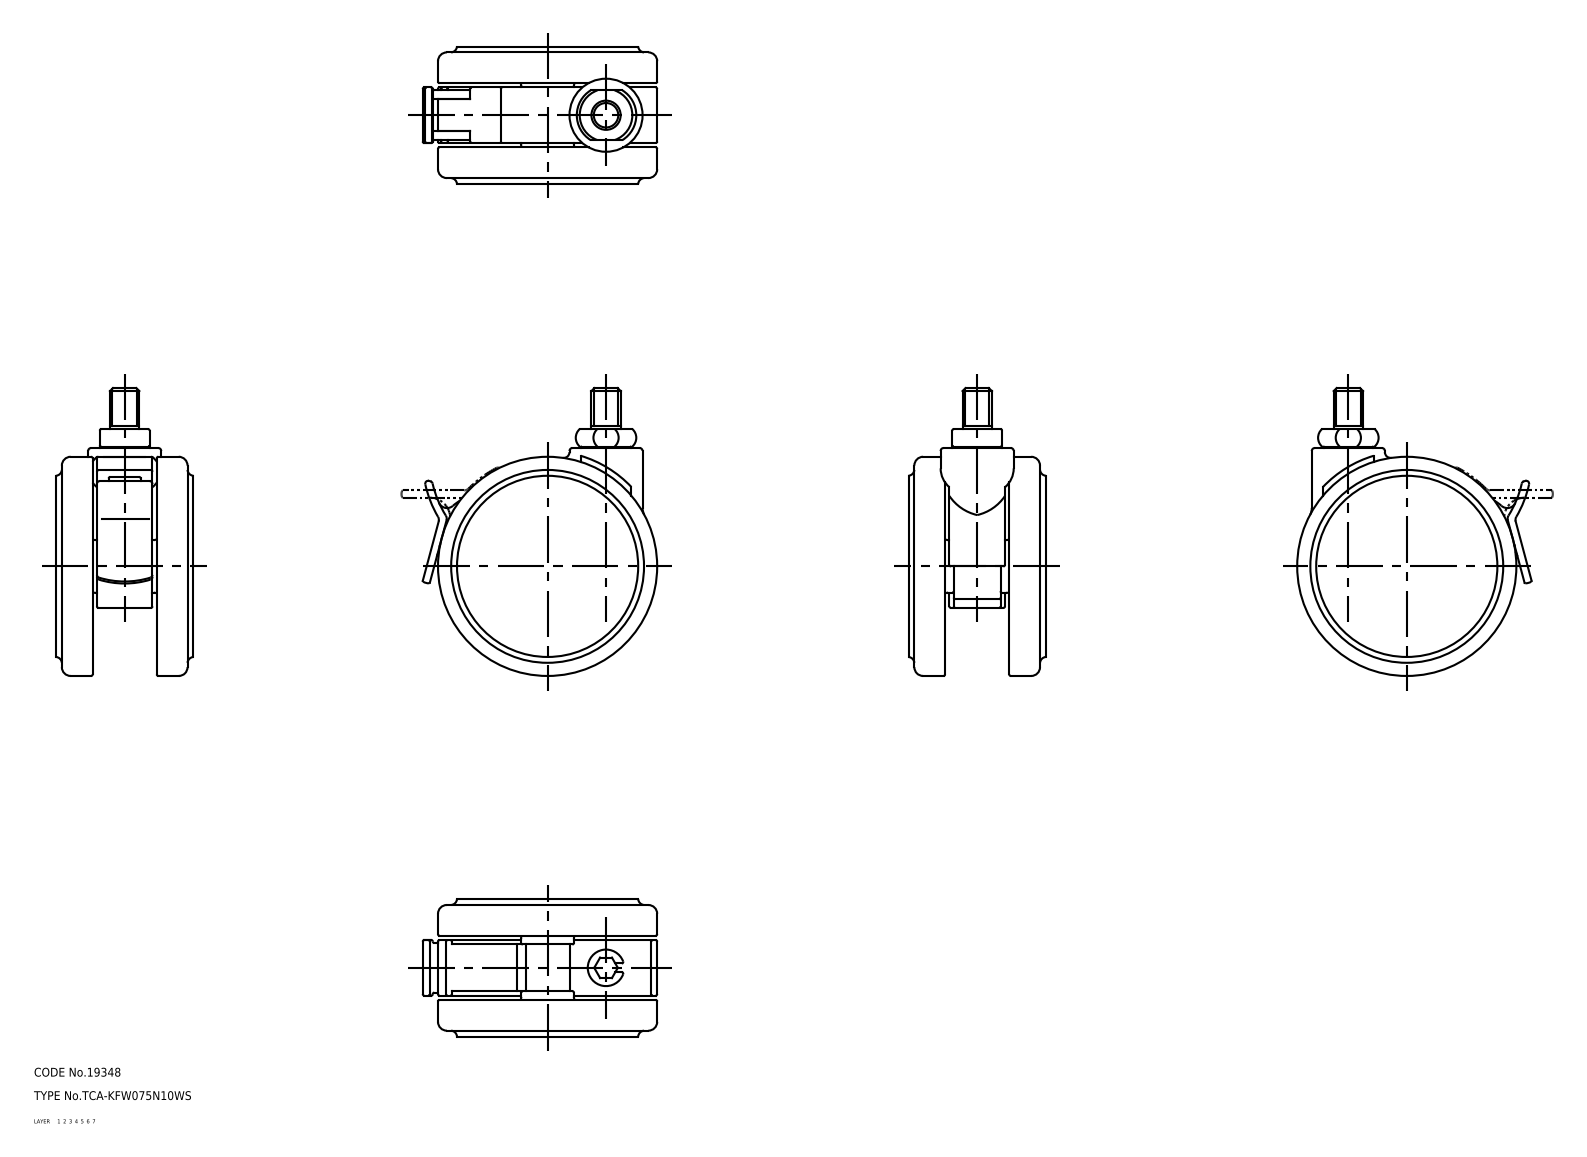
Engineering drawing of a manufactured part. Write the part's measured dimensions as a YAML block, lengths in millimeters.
part_name: "main shaft; wheel; wheel_mr; lever (+1 more)"
step_written_by: "SolidWorks 2015 (AUTOMOTIVE_DESIGN)"
units: millimeters
bodies: {solids: 5, faces: 269, planar: 62, cylindrical: 107, other: 100}
overall_size: [98.5, 80.25, 47]
volume: 155448
surface_area: 39518
round_holes:
  - {diameter: 6, count: 1}
  - {diameter: 43, count: 1}
round_bosses_or_shafts:
  - {diameter: 75, count: 1}
  - {diameter: 25, count: 1}
  - {diameter: 18, count: 1}
  - {diameter: 17, count: 1}
  - {diameter: 12.5, count: 1}
  - {diameter: 10, count: 1}
partial_cylinders:
  - {radius: 0.5, count: 43}
  - {radius: 1, count: 2}
  - {radius: 2, count: 2}
  - {radius: 3, count: 2}
  - {radius: 35.5, count: 2}
  - {radius: 2.89, count: 1}
  - {radius: 7, count: 1}
  - {radius: 7.54, count: 1}
face_to_face_distances: [12.5, 34.5, 1.5, 22, 3, 14, 19, 20.5, 47, 33]
